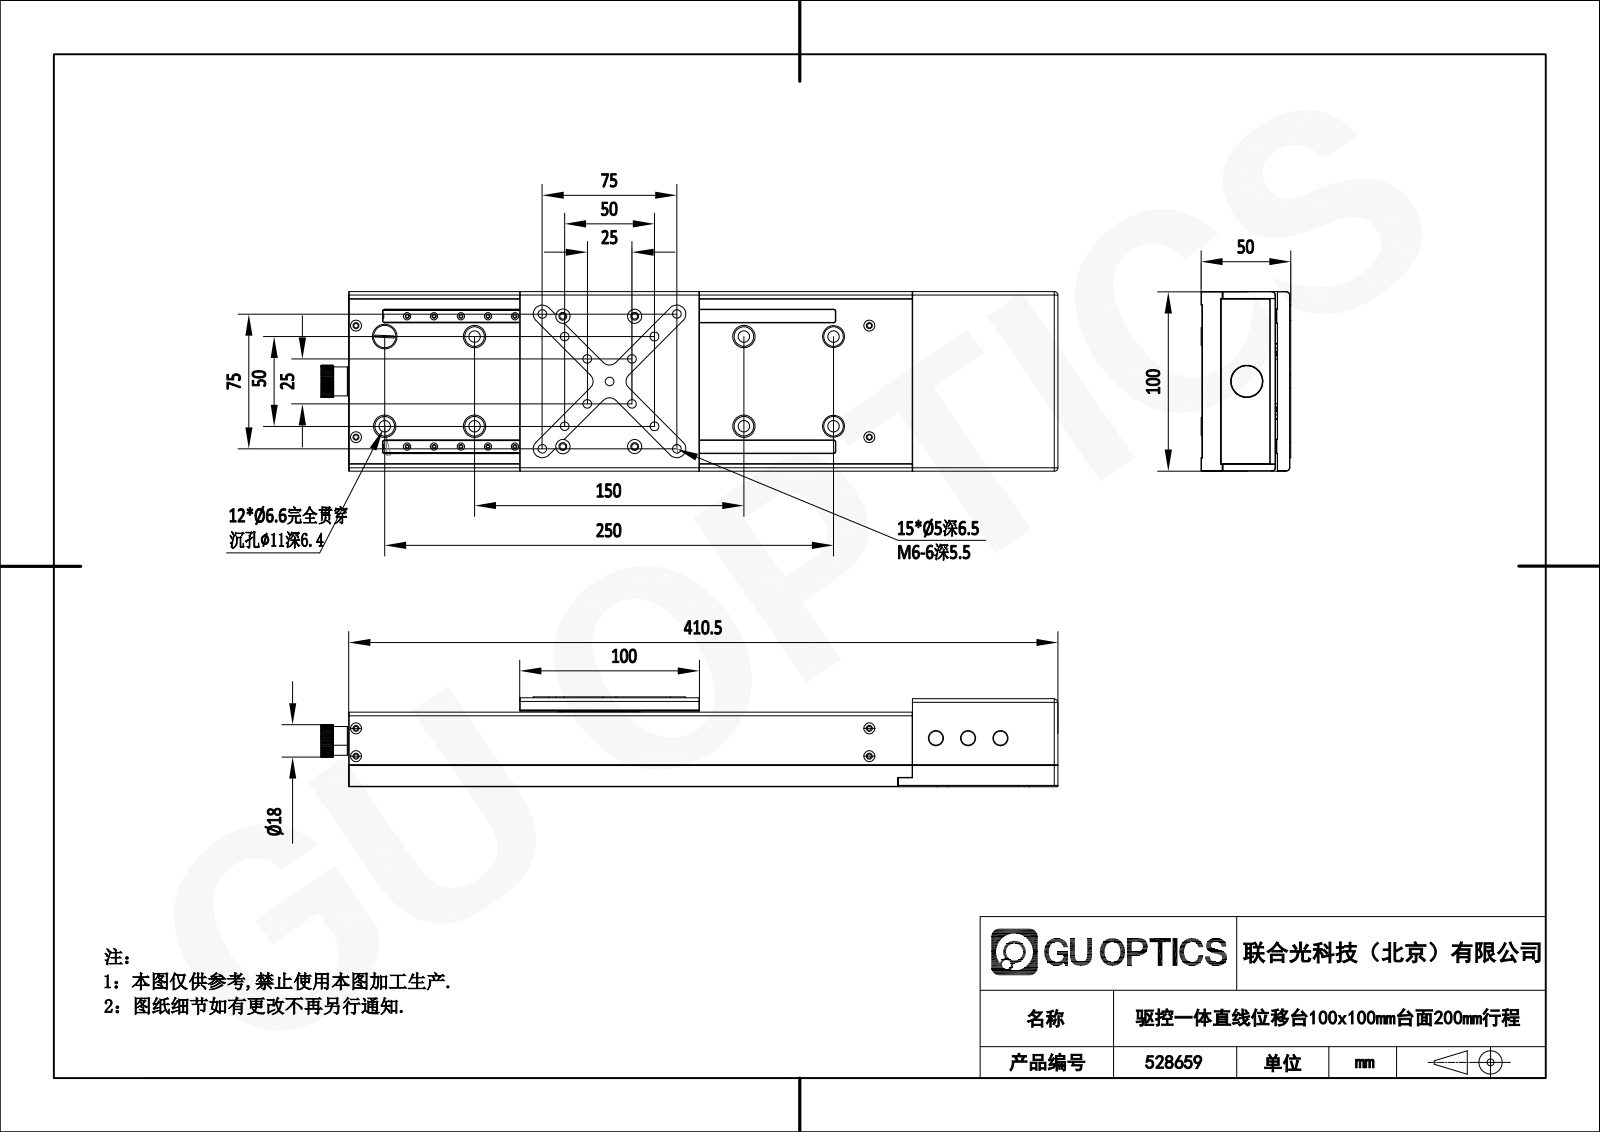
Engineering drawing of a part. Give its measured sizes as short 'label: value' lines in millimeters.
name: 528659
written by: SolidWorks 2020 (CONFIG_CONTROL_DESIGN)
unit: mm
bodies: 47 solids, 2410 faces (1228 planar, 820 cylindrical, 362 other)
size: 410.5 × 100 × 50
volume: 1 025 000 mm³; area: 351 941 mm²
holes: 32× ⌀2.4, 21× ⌀2.5, 21× ⌀3.4, 18× ⌀4.2, 17× ⌀1.57, 16× ⌀1.6, 16× ⌀4.4, 14× ⌀5, 12× ⌀12.5, 10× ⌀6.6, 10× ⌀11, 9× ⌀6.5
bosses: 4× ⌀2.2, 2× ⌀14, 2× ⌀3.8, 2× ⌀2, 1× ⌀22, 1× ⌀16, 1× ⌀13, 1× ⌀3
rounds: 29× R2, 20× R1, 12× R5, 4× R0.7, 4× R1.35, 2× R0.3, 2× R0.4, 2× R0.5
face distances: 4, 38, 26.5, 11.5, 3, 1, 0.5, 30.5, 41, 29.5
hole spacings: 10.5, 15, 8, 12, 14.42, 30, 45, 72.6
